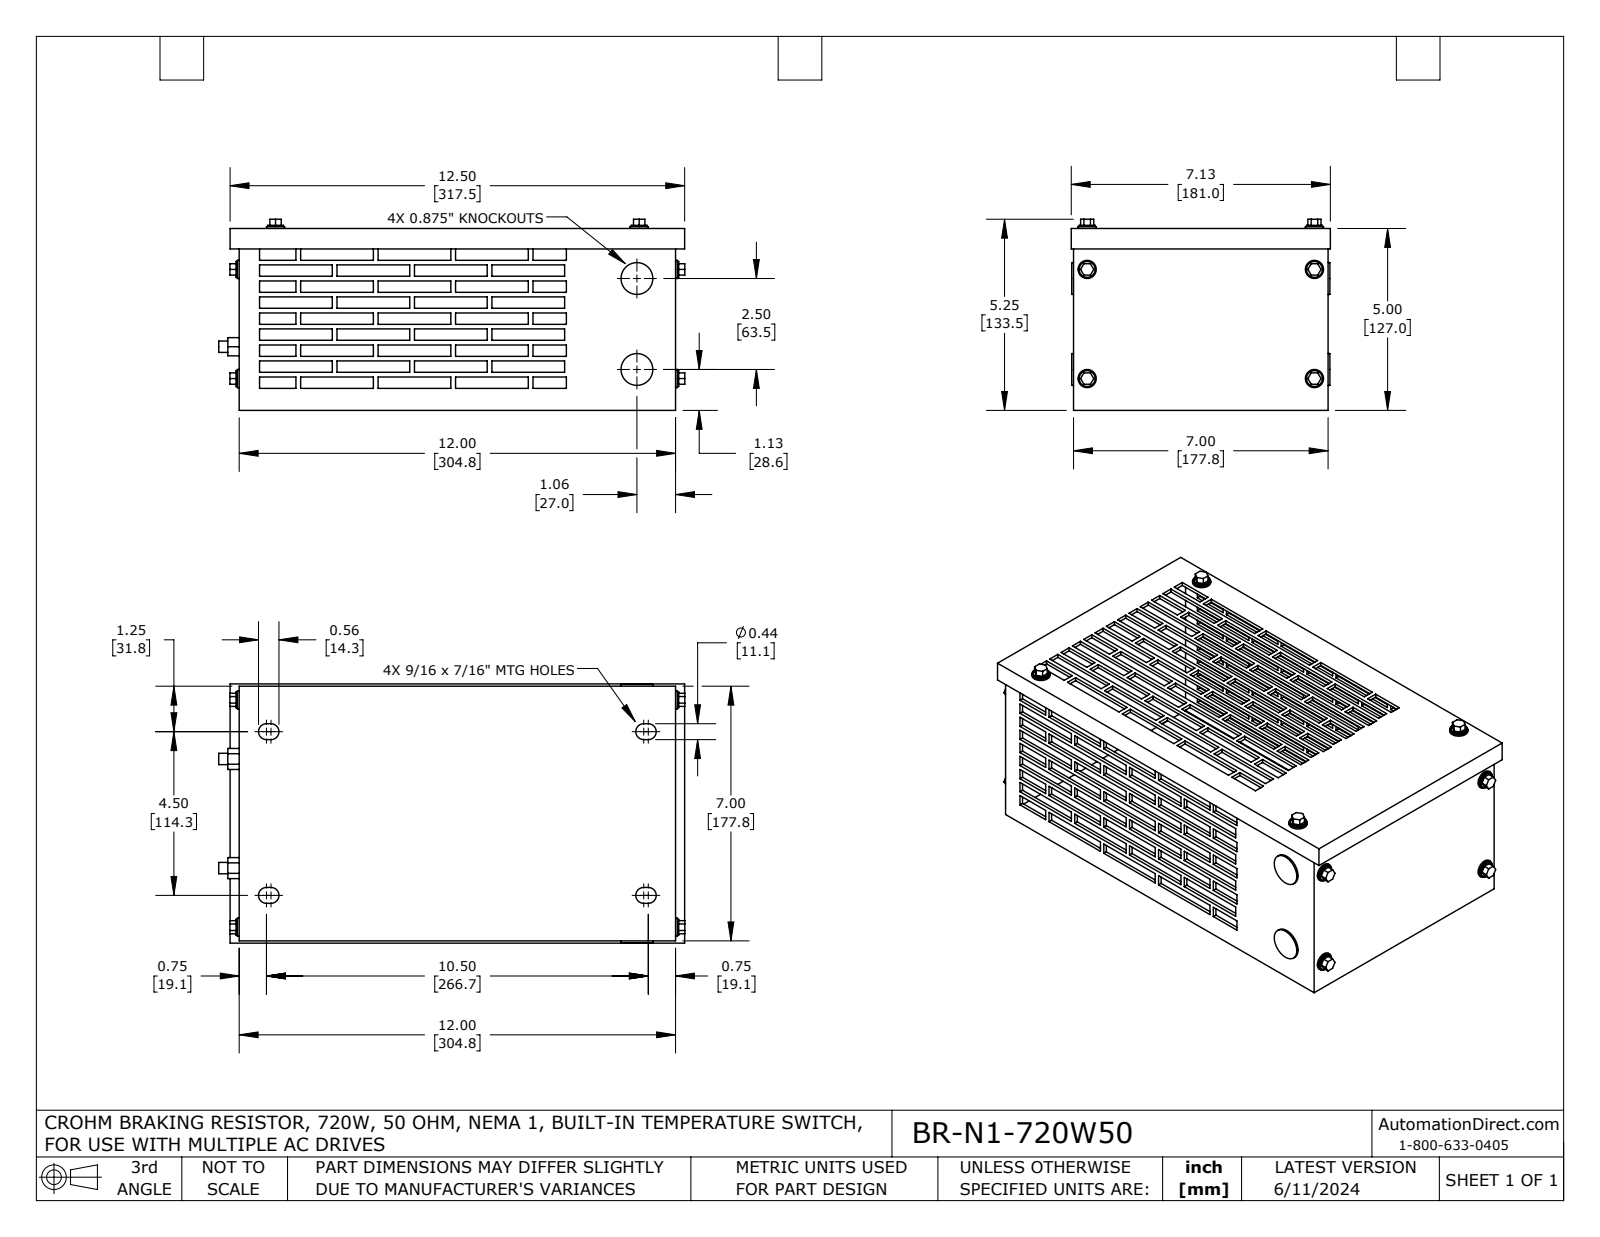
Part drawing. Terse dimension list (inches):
name: BR-N1-720W50
written by: SolidWorks 2021 (AUTOMOTIVE_DESIGN)
unit: in
bodies: 31 solids, 846 faces (746 planar, 100 cylindrical, 0 other)
size: 12.817 × 7.125 × 5.254
volume: 28.59 in³; area: 639.2 in²
holes: 8× ⌀0.25, 2× ⌀0.75
bosses: 8× ⌀0.5, 8× ⌀0.437, 2× ⌀0.875, 2× ⌀0.313
rounds: 8× R0.219
face distances: 0.1, 4.9, 11.9, 6.9, 5, 4.8, 12, 7, 11.8, 6.8
hole spacings: 6.25, 3, 6.933, 10, 11.793, 2.5
